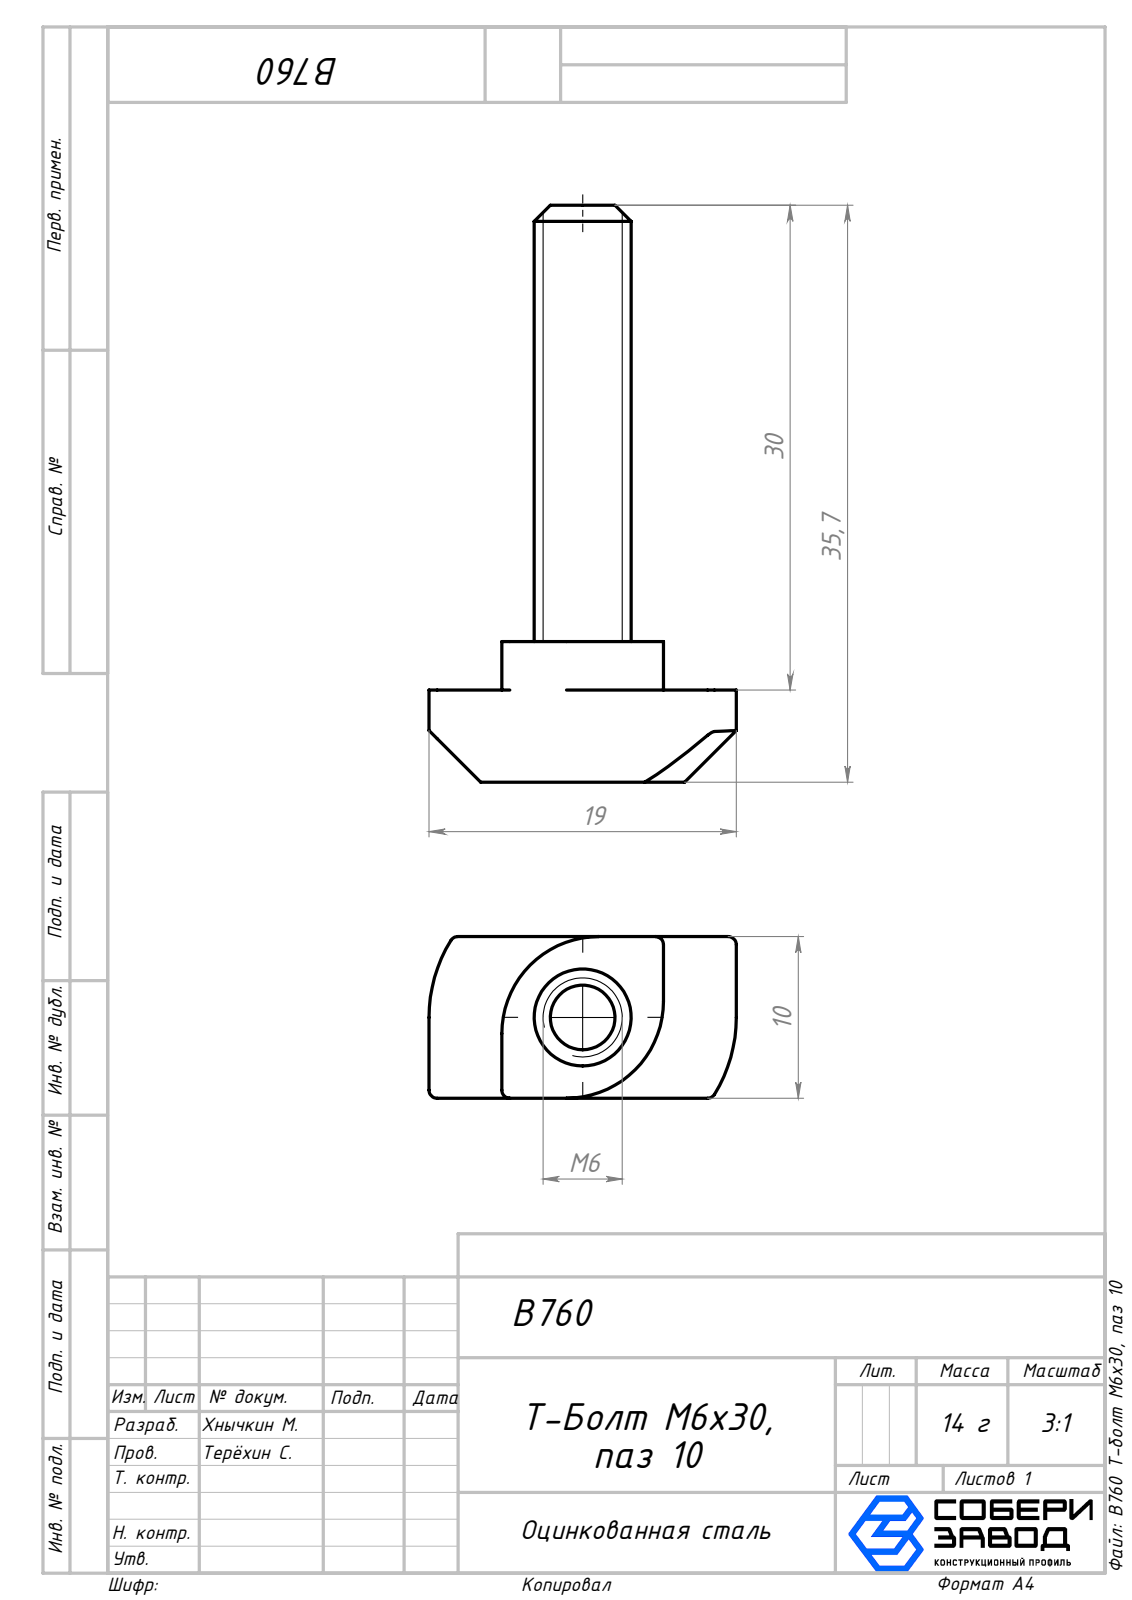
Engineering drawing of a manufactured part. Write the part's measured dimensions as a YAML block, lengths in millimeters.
part_name: "B760 Т-болт М6х30, паз 10"
step_written_by: "SolidWorks 2026 (AUTOMOTIVE_DESIGN)"
units: millimeters
bodies: {solids: 1, faces: 29, planar: 13, cylindrical: 12, other: 4}
overall_size: [35.7, 19, 10]
volume: 1958
surface_area: 1225
round_bosses_or_shafts:
  - {diameter: 6, count: 1}
partial_cylinders:
  - {radius: 0.5, count: 6}
  - {radius: 6, count: 2}
  - {radius: 9.08, count: 2}
face_to_face_distances: [10, 5.7, 8.7, 3, 4.5, 14.5, 35.7, 30, 27, 19]
